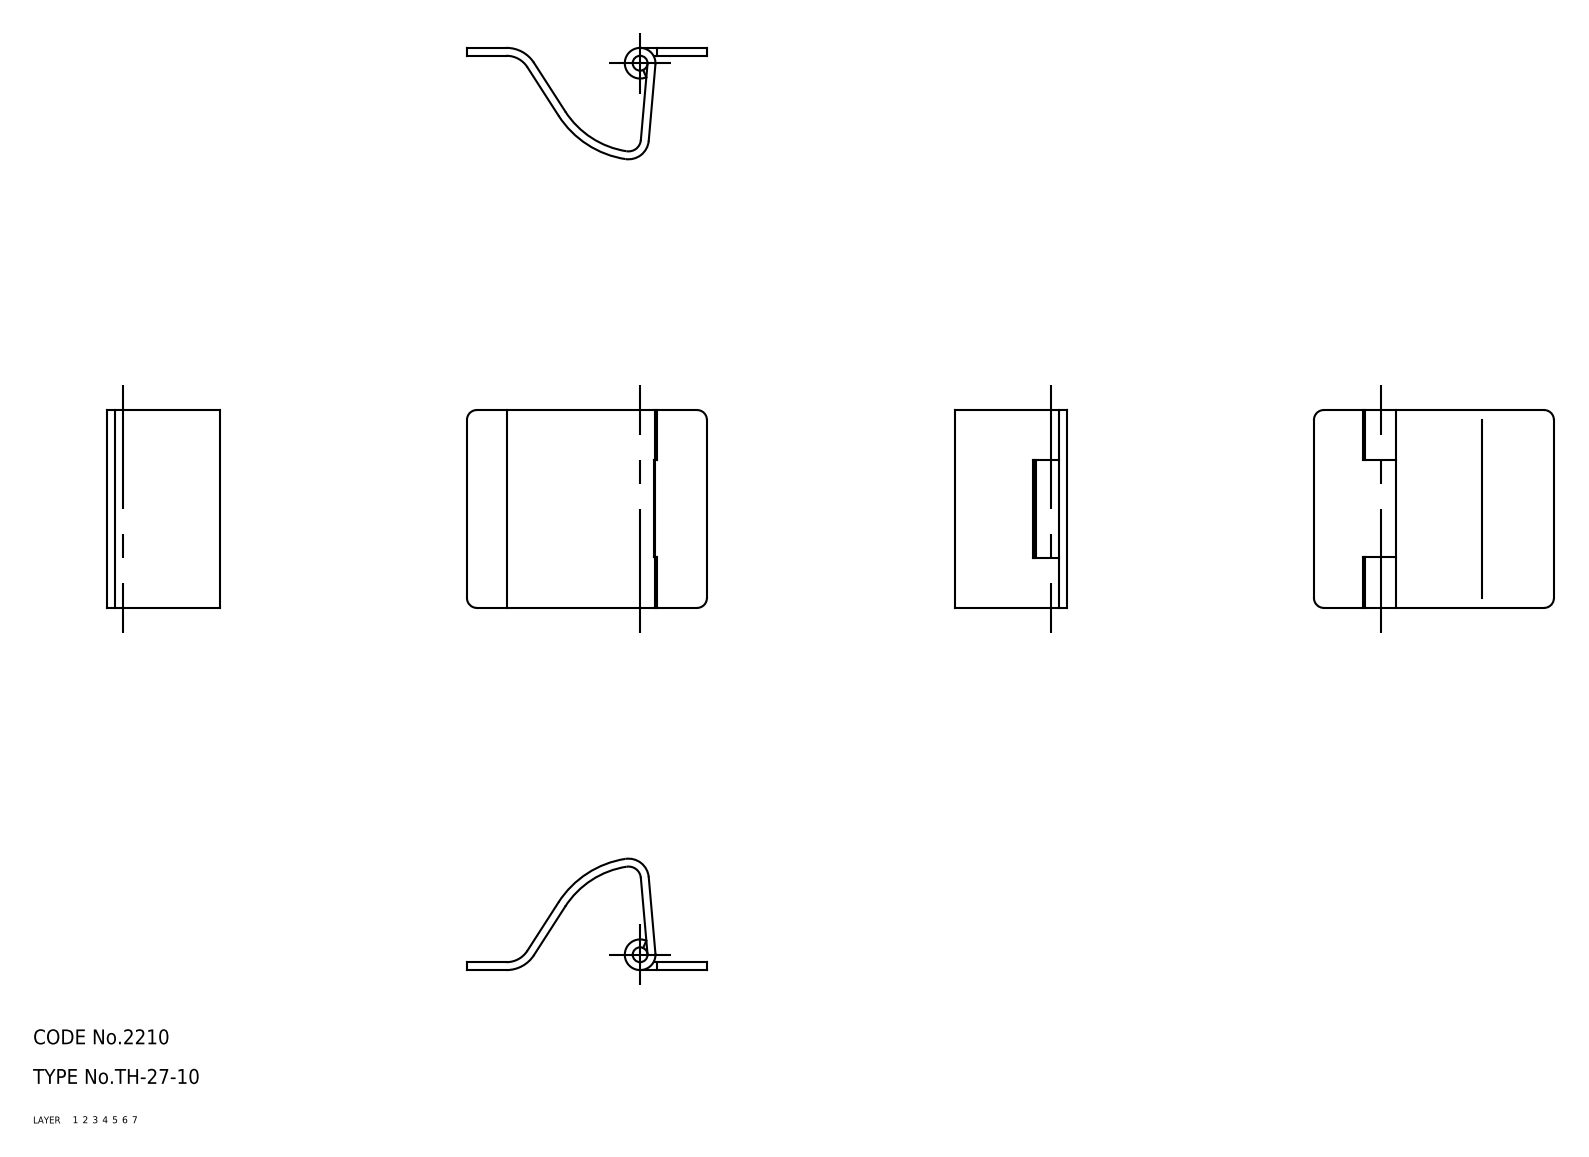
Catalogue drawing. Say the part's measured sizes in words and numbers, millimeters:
The part is named "shaft; hinge piece_B; hinge piece_A; TH_27_10_6711_36". Its 3-D file was written by "CADfix (AUTOMOTIVE_DESIGN)". It is 3 solids with 44 faces: 0 planar, 0 cylindrical and 44 other. Overall it measures 48.5 by 40 by 22.52 millimeters. Its volume is 5 658 cubic millimeters and its surface area 7 730 square millimeters.
